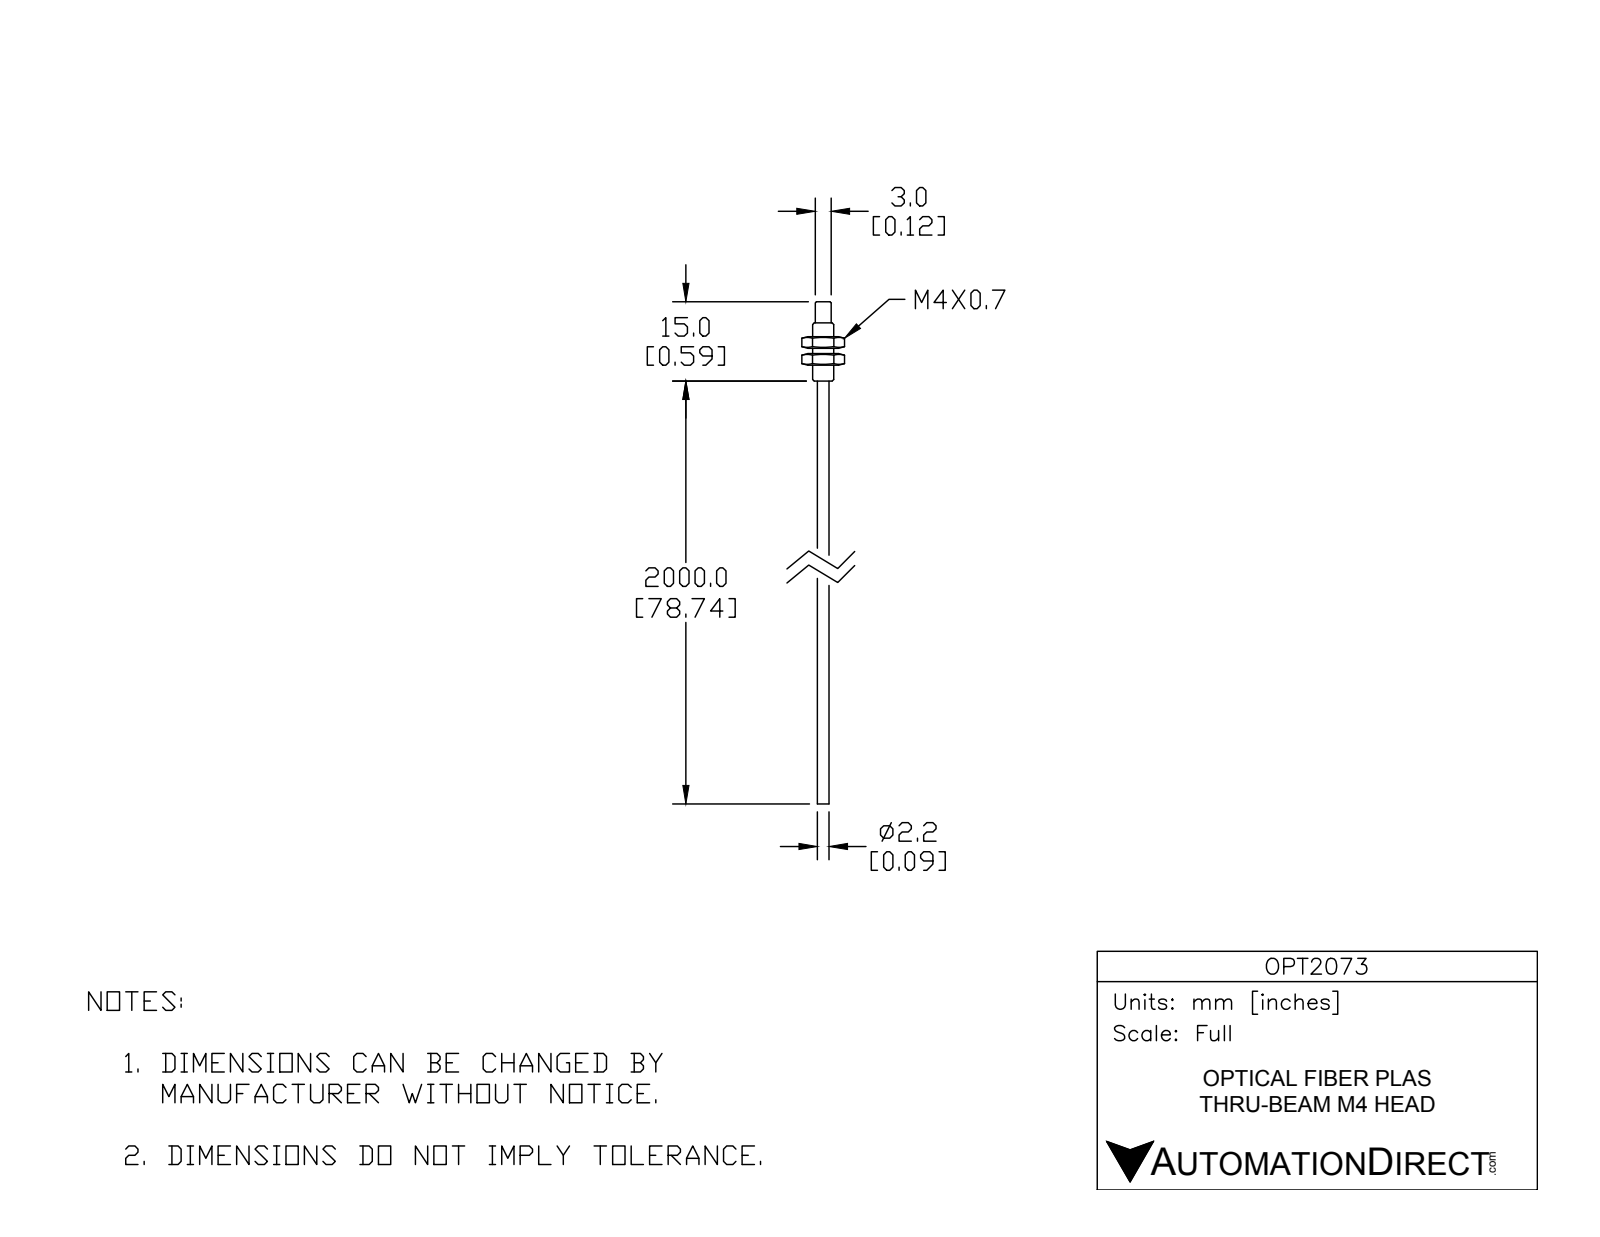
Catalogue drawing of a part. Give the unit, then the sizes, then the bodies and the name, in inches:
Units: inches
Overall size (bounding box): 3.74 × 0.318 × 0.276
Round bosses / shafts (diameter × count): ⌀0.157 ×1, ⌀0.118 ×1, ⌀0.087 ×1
Main face-to-face distances: 0.276, 0.087, 0.126, 0.213, 0.039, 0.26, 0.346, 0.386, 0.472, 0.591
Volume: 0.035 in³ · Surface area: 1.334 in²
Bodies: 2 solids, 48 faces (22 planar, 12 cylindrical, 14 other)
Part name (STEP PRODUCT): OPT2073
STEP written by: SolidWorks 2014 (AUTOMOTIVE_DESIGN)
